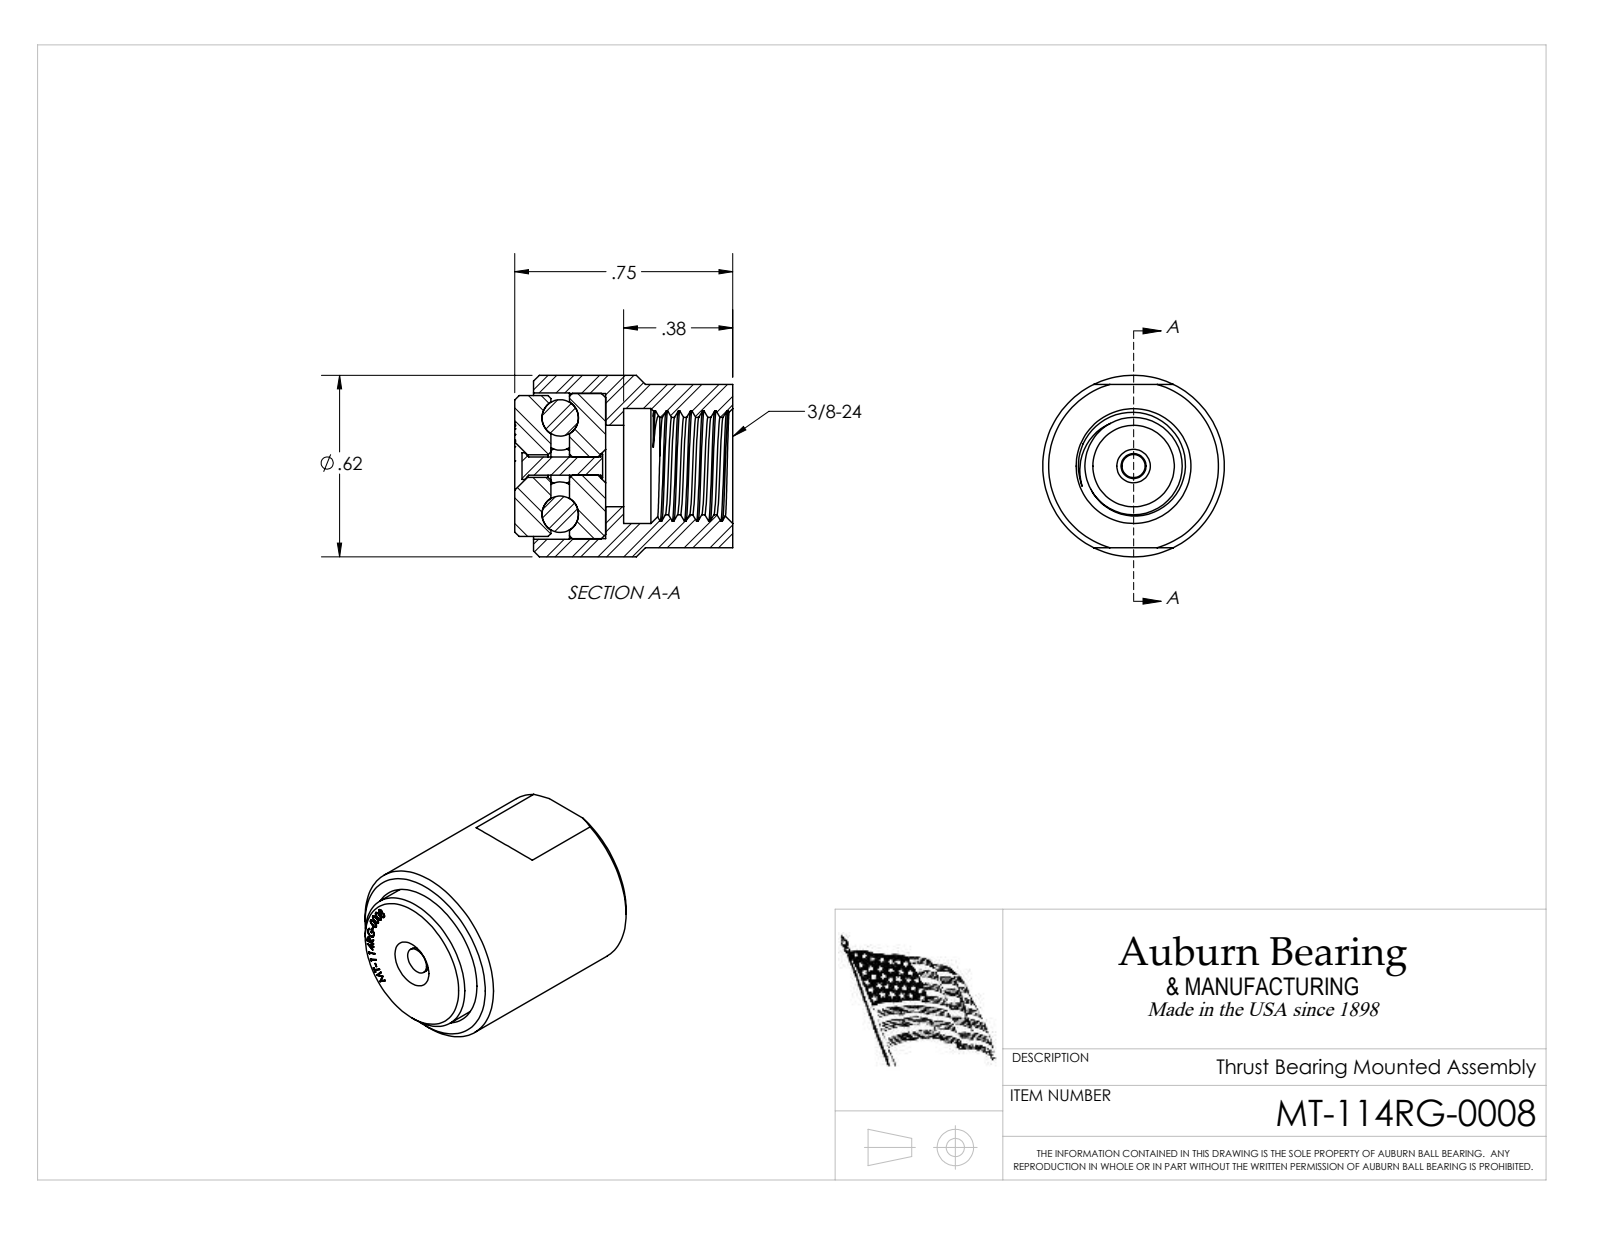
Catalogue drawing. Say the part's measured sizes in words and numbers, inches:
The part is named "MT-114RG-0008". Its 3-D file was written by "SolidWorks 2020 (CONFIG_CONTROL_DESIGN)". It is 12 solids with 252 faces: 107 planar, 34 cylindrical and 111 other. Overall it measures 0.749 by 0.624 by 0.624 inches. Its volume is 0.162 cubic inches and its surface area 4.483 square inches. Round holes: 1 of diameter 0.062, 1 of diameter 0.078, 1 of diameter 0.28, 1 of diameter 0.334, 1 of diameter 0.395, 1 of diameter 0.499, 1 of diameter 0.503. Round bosses or shafts: 1 of diameter 0.624, 1 of diameter 0.5, 1 of diameter 0.484, 1 of diameter 0.091. The main face-to-face distances are 0.437, 0.312, 0.749, 0.124, 0.188, 0.561, 0.065, 0.247, 0.684, 0.123.
